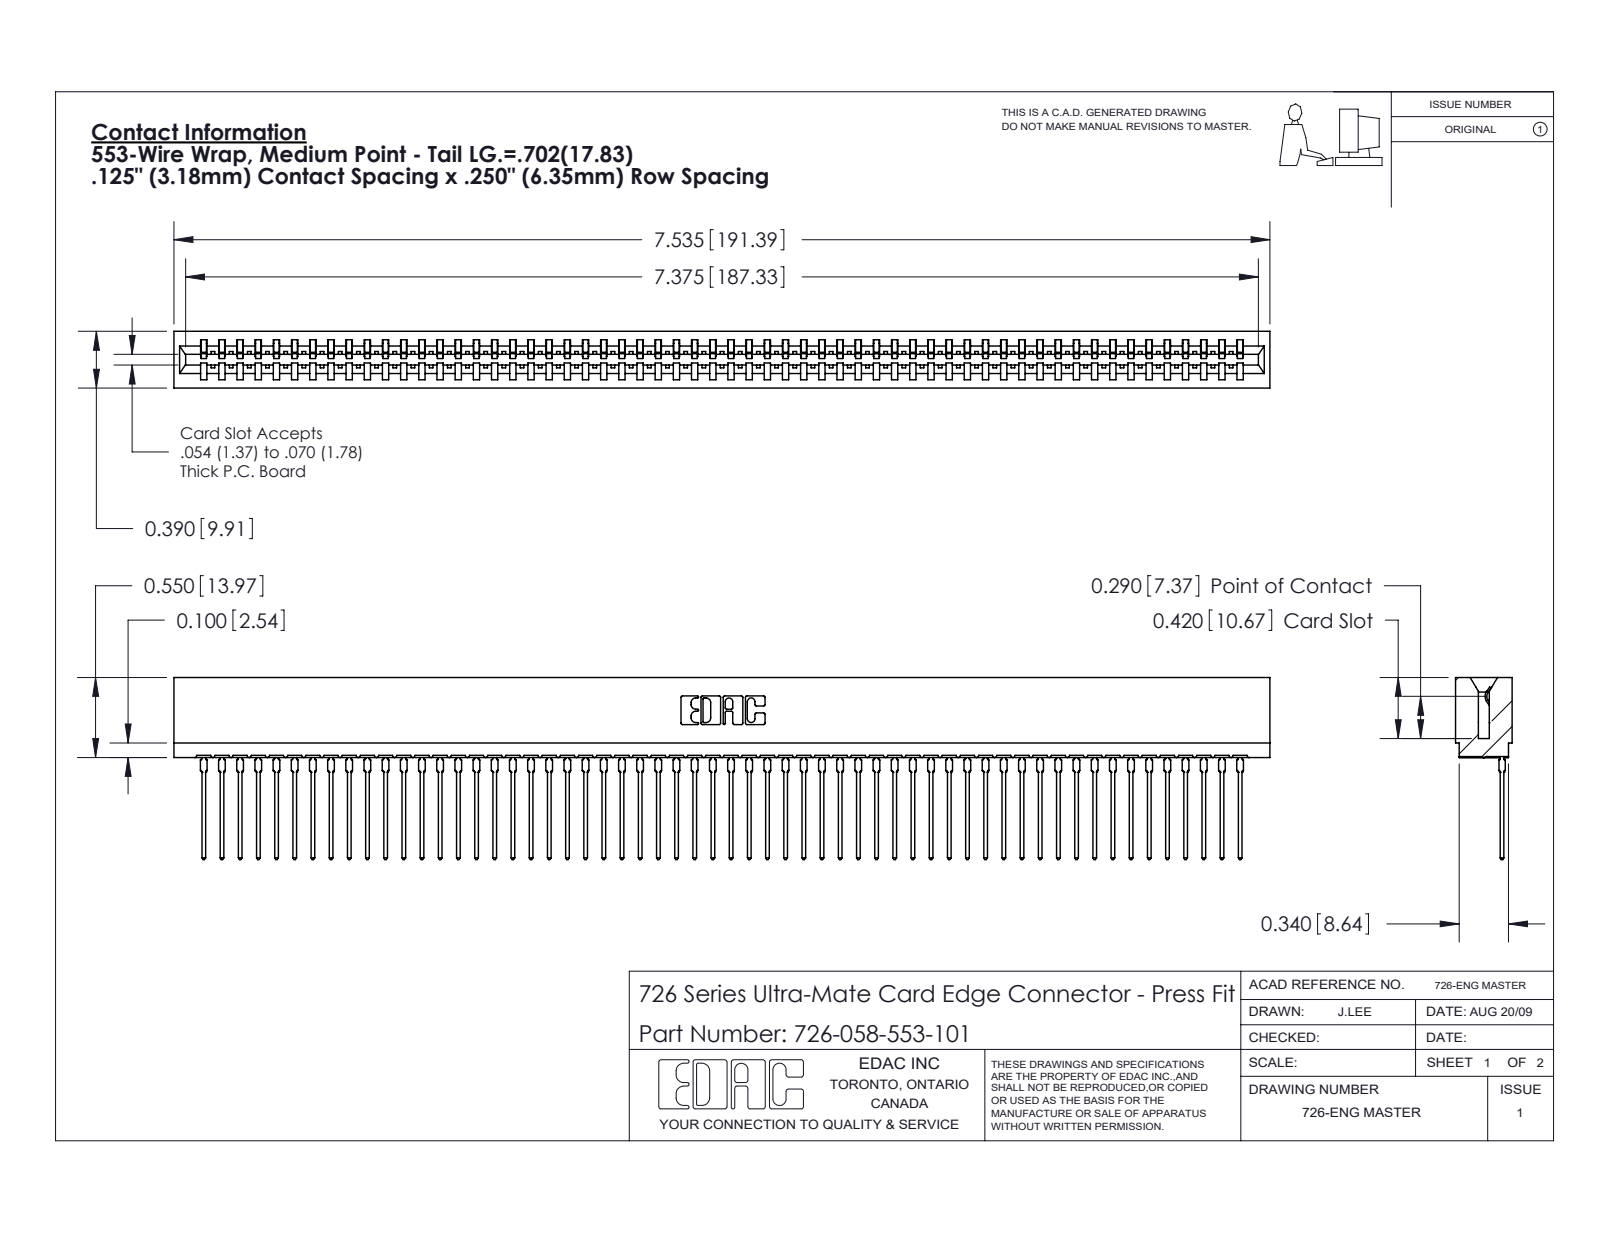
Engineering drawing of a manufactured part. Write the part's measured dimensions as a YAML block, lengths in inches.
part_name: "746-292-001_553; 726-058-553-101; 726 Part_.515 Slot Depth - 01"
step_written_by: "SolidWorks 2020 (CONFIG_CONTROL_DESIGN)"
units: inches
bodies: {solids: 59, faces: 6361, planar: 3709, cylindrical: 1144, other: 1508}
overall_size: [7.535, 1.251, 0.39]
volume: 1.051
surface_area: 42.75
partial_cylinders:
  - {radius: 0.021, count: 116}
  - {radius: 0.015, count: 59}
  - {radius: 0.01, count: 22}
  - {radius: 0.007, count: 6}
  - {radius: 0.031, count: 6}
  - {radius: 0.005, count: 4}
  - {radius: 0.011, count: 4}
  - {radius: 0.026, count: 3}
face_to_face_distances: [0.057, 0.333, 0.39, 0.025, 0.307, 0.25, 0.083, 0.275, 0.365, 0.032]
